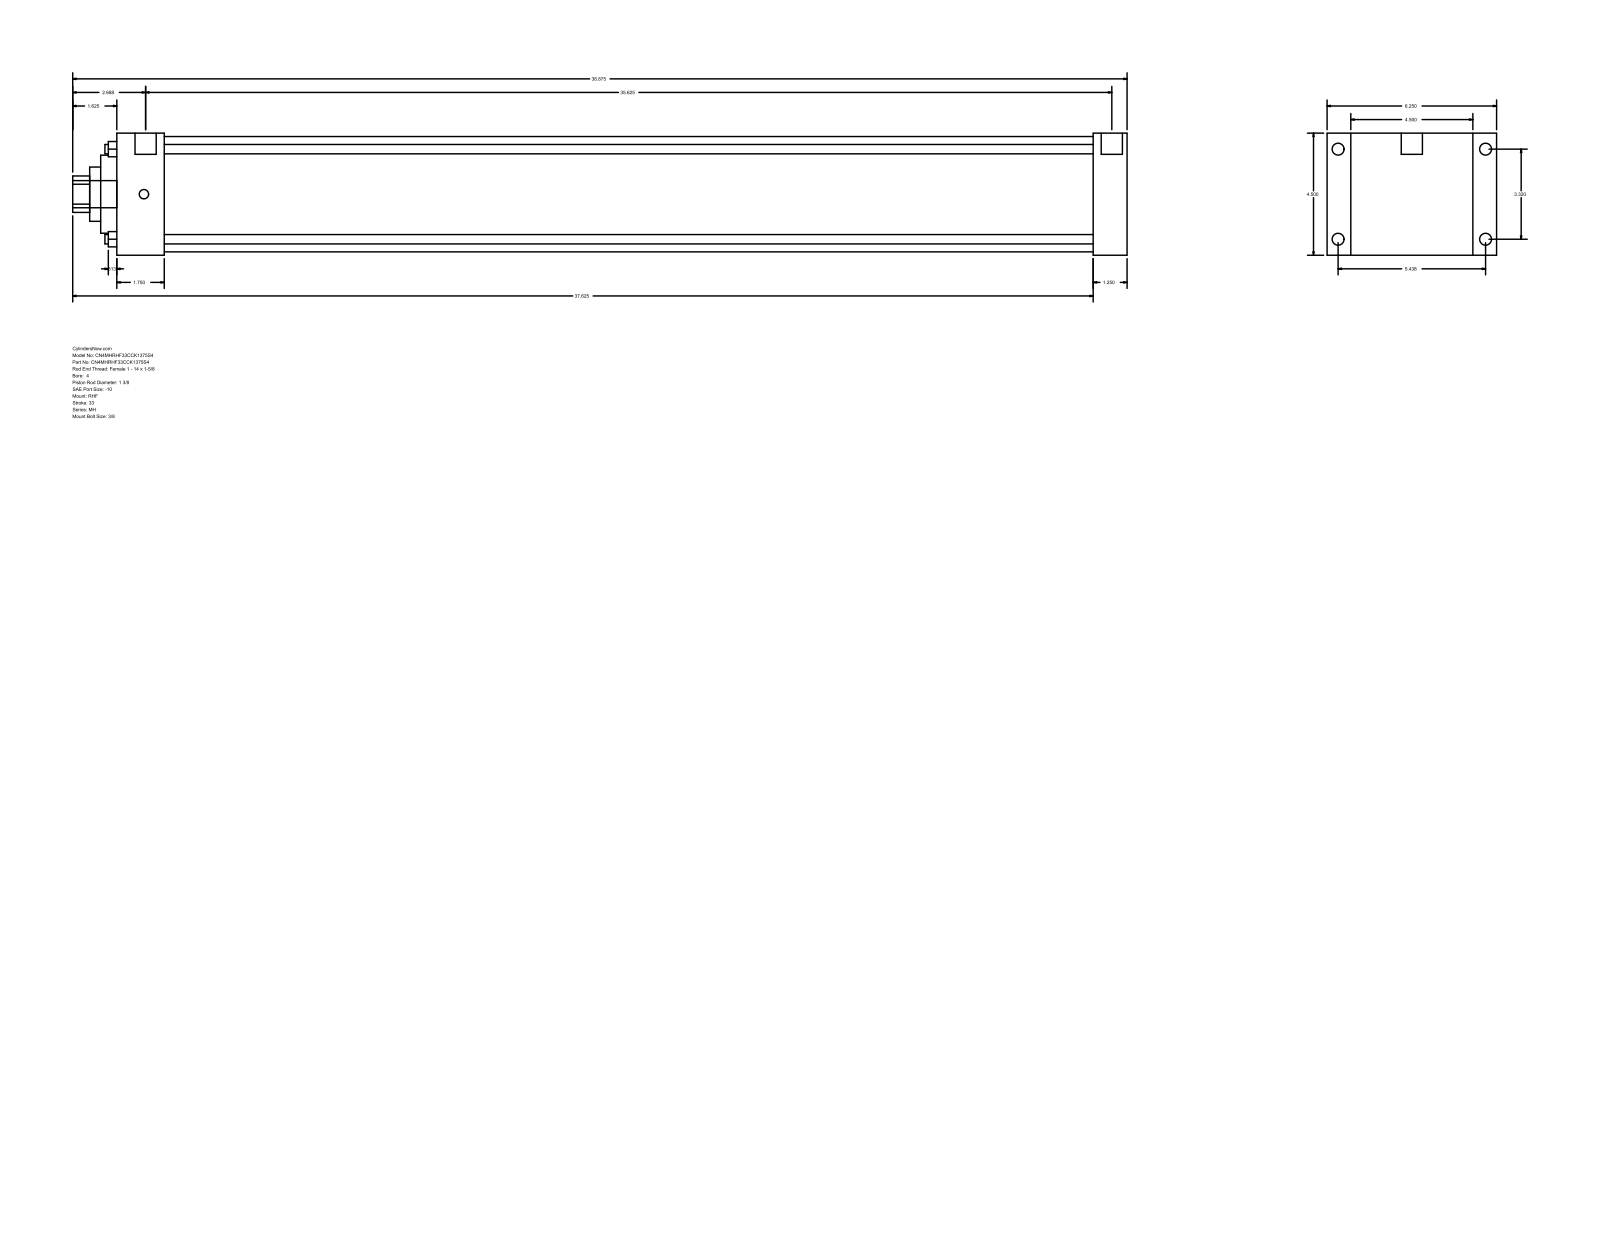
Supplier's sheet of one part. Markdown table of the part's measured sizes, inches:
| quantity | value |
| --- | --- |
| part name | MH_RHF__0400_1.375 |
| STEP written by | GSSL Pune (CONFIG_CONTROL_DESIGN) |
| units | inches |
| bodies | 0 solids, 90 faces (61 planar, 29 cylindrical, 0 other) |
| overall size | 38.875 × 6.25 × 4.5 |
| round holes (diameter × count) | 0.345 × 4, 1.375 × 1, 2 × 1, 2.875 × 1, 4.25 × 1 |
| round bosses / shafts (diameter × count) | 0.438 × 4, 0.344 × 4, 0.781 × 2, 1 × 1 |
| partial cylindrical surfaces (radius × count) | 0.672 × 1 |
| main face-to-face distances | 4.5, 37.25, 36, 1.25, 0.875, 5.375, 1.75, 34.25, 35.5, 6.25 |
| hole center spacings | 2.347, 3.32, 4.695 |
